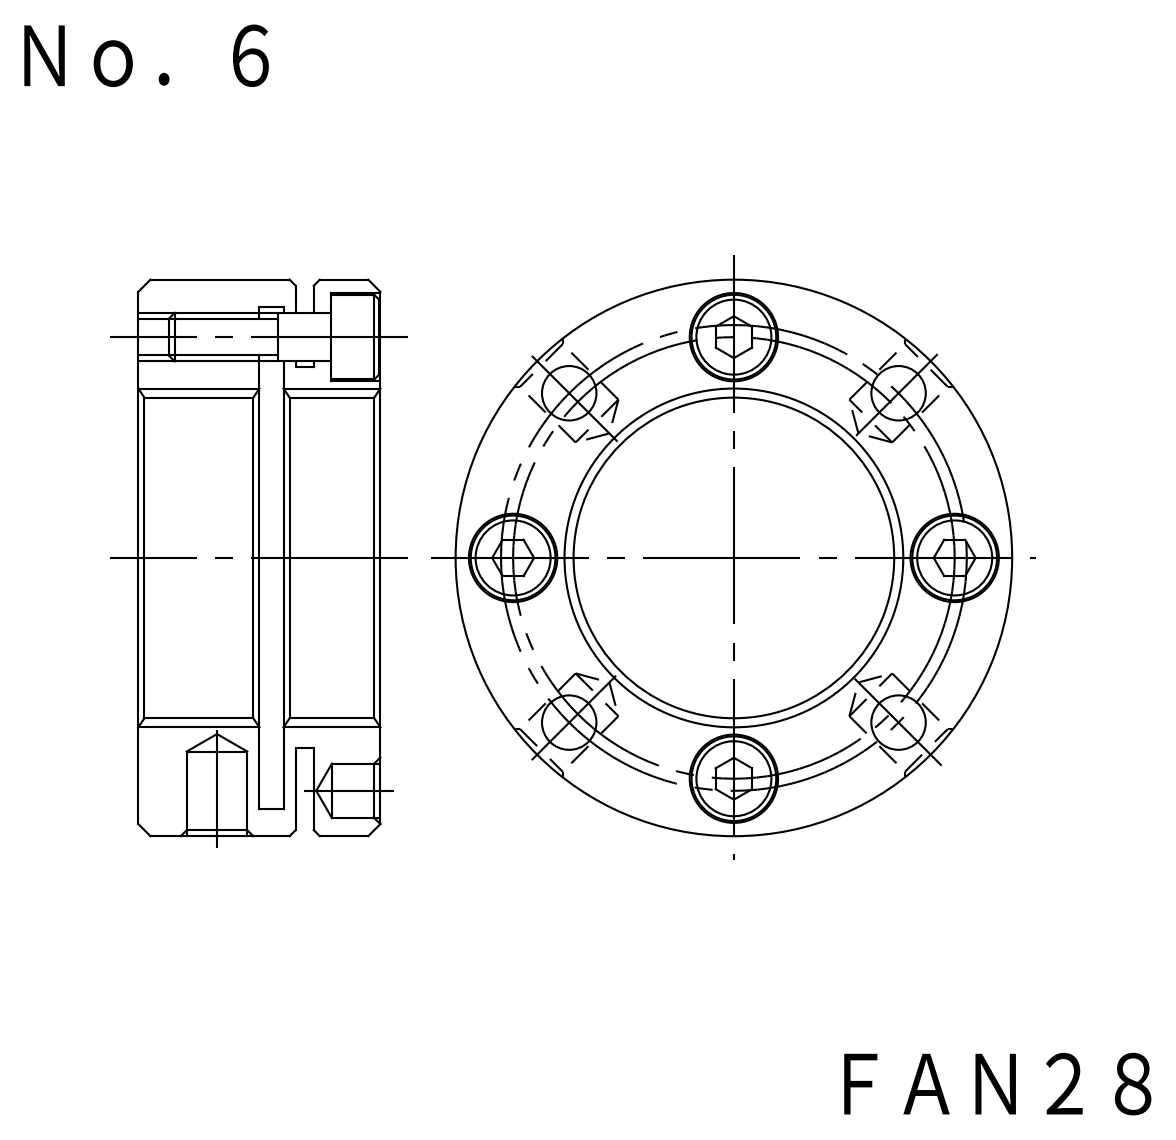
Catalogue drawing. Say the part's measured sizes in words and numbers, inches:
The part is named "FKD FAN28; M4X14_default". Its 3-D file was written by "SolidWorks 2012 (CONFIG_CONTROL_DESIGN)". It is 5 solids with 142 faces: 50 planar, 76 cylindrical and 16 other. Overall it measures 1.811 by 1.811 by 0.787 inches. Its volume is 1.037 cubic inches and its surface area 19.59 square inches. Round holes: 4 of diameter 0.128, 4 of diameter 0.169, 4 of diameter 0.177, 4 of diameter 0.287, 2 of diameter 0.197, 1 of diameter 1.102, 1 of diameter 1.654. Round bosses or shafts: 4 of diameter 0.276, 4 of diameter 0.157, 1 of diameter 1.811, 1 of diameter 1.26. The main face-to-face distances are 0.079, 0.118, 0.787, 0.484, 0.303, 0.563, 0.224, 0.366, 0.197, 0.421. The hole center spacings are 0.569, 1.373, 0.728, 0.758, 1.03, 1.072, 1.457, 1.515.
